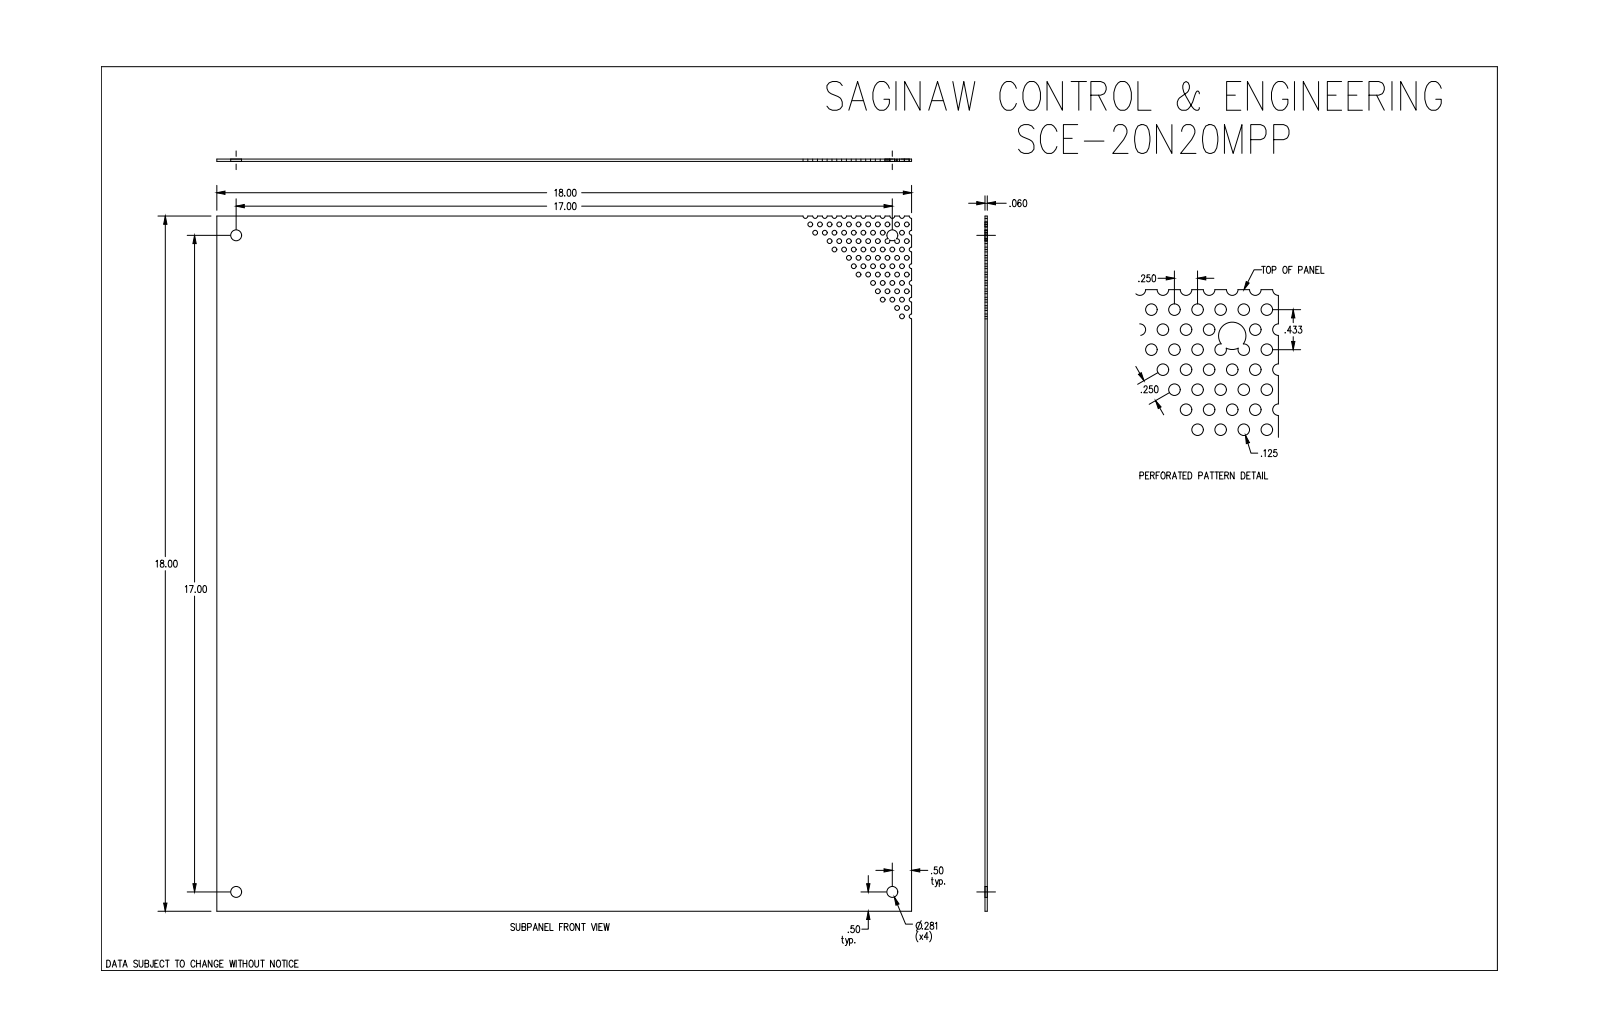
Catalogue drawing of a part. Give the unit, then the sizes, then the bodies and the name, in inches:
Units: inches
Overall size (bounding box): 18 × 18 × 0.06
Round holes (diameter × count): ⌀0.125 ×70, ⌀0.281 ×4
Partial cylindrical surfaces — rounded edges, fillets, slot ends (radius × count): R0.062 ×18
Main face-to-face distances: 0.06, 18
Hole centre spacings: 0.25, 0.661, 0.5, 0.433, 0.433, 1.323, 1.09, 0.75
Volume: 19.37 in³ · Surface area: 651.8 in²
Bodies: 1 solid, 116 faces (23 planar, 93 cylindrical, 0 other)
Part name (STEP PRODUCT): SCE-20N20MPP
STEP written by: SolidWorks 2019 (CONFIG_CONTROL_DESIGN)
